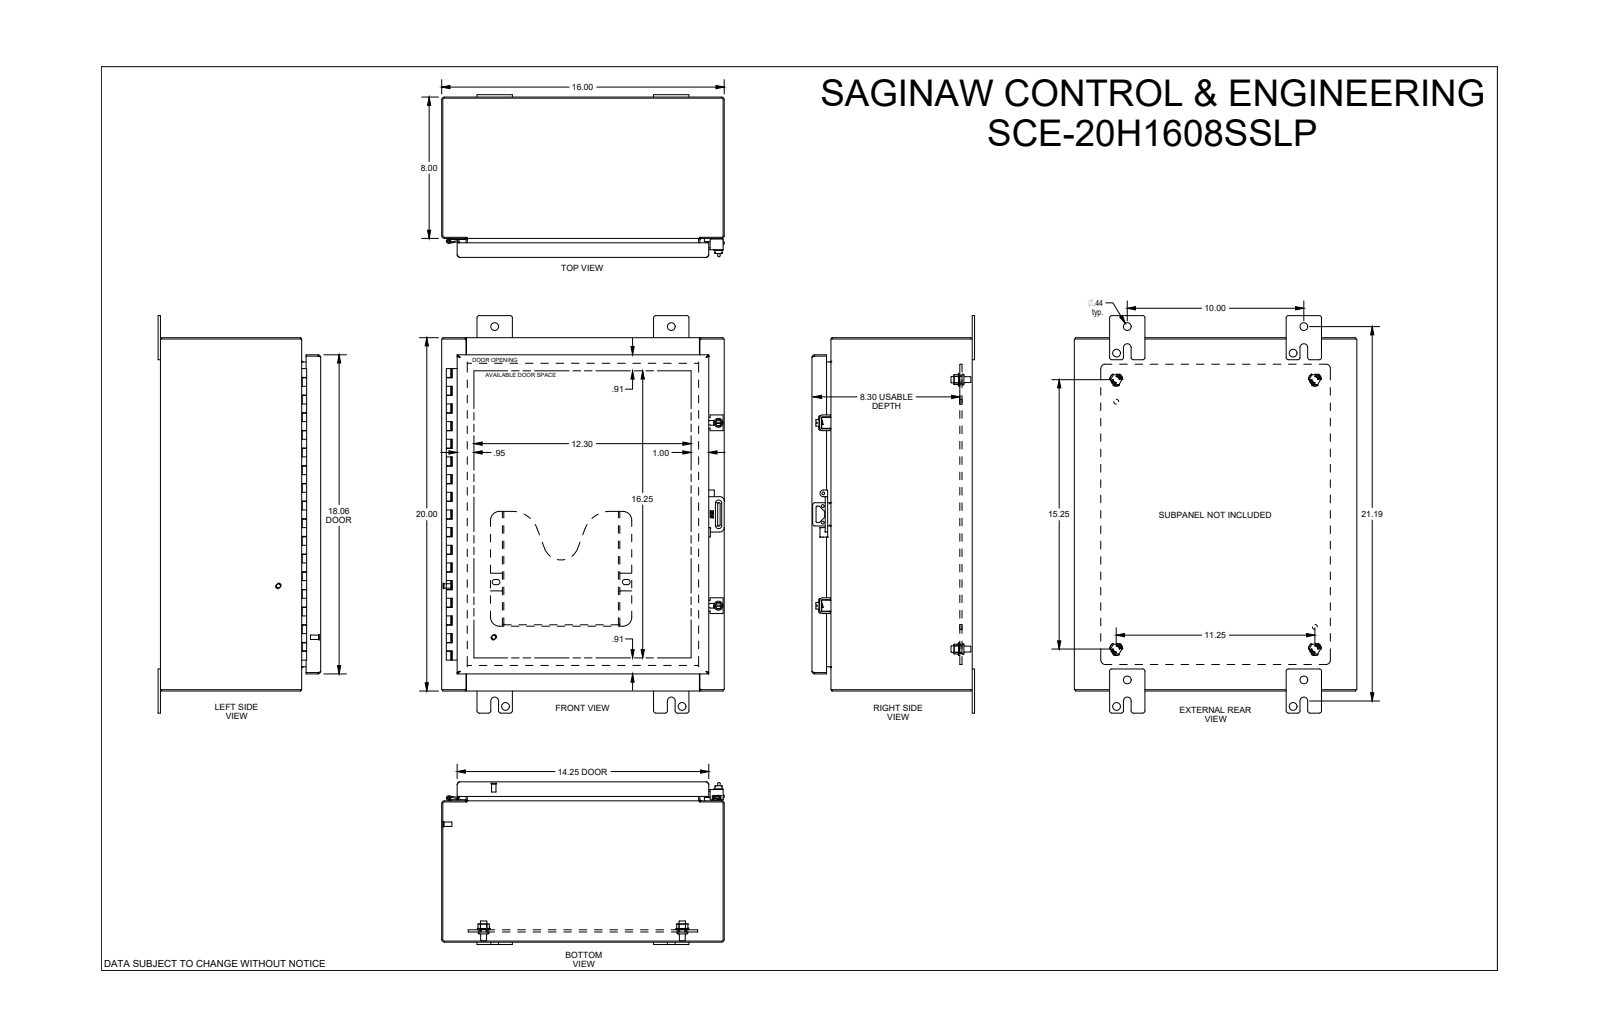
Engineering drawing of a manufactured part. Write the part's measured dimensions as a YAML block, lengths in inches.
part_name: "SCE-20H1608LP"
step_written_by: "SolidWorks 2021 (AUTOMOTIVE_DESIGN)"
units: inches
bodies: {solids: 36, faces: 1903, planar: 737, cylindrical: 796, other: 370}
overall_size: [22.5, 16, 9.343]
volume: 146.3
surface_area: 3487
round_holes:
  - {diameter: 0.172, count: 4}
  - {diameter: 0.205, count: 4}
  - {diameter: 0.218, count: 4}
  - {diameter: 0.244, count: 4}
  - {diameter: 0.312, count: 4}
  - {diameter: 0.375, count: 4}
  - {diameter: 0.437, count: 4}
  - {diameter: 0.5, count: 4}
  - {diameter: 0.04, count: 2}
  - {diameter: 0.16, count: 2}
  - {diameter: 0.188, count: 2}
  - {diameter: 0.203, count: 2}
round_bosses_or_shafts:
  - {diameter: 0.25, count: 6}
  - {diameter: 0.248, count: 6}
  - {diameter: 0.59, count: 4}
  - {diameter: 0.376, count: 4}
  - {diameter: 0.375, count: 4}
  - {diameter: 0.33, count: 4}
  - {diameter: 0.31, count: 4}
  - {diameter: 0.24, count: 4}
partial_cylinders:
  - {radius: 0.025, count: 68}
  - {radius: 0.01, count: 62}
  - {radius: 0.03, count: 32}
  - {radius: 0.06, count: 26}
  - {radius: 0.015, count: 24}
  - {radius: 0.185, count: 21}
  - {radius: 0.04, count: 18}
  - {radius: 0.22, count: 16}
face_to_face_distances: [0.075, 0.06, 8.993, 15.925, 9.068, 9.008, 8.933, 19.925, 0.575, 0.5]
hole_center_spacings: [16.887, 18.5, 1.375, 1.741, 1.741, 2.942, 4.916, 9.999]
